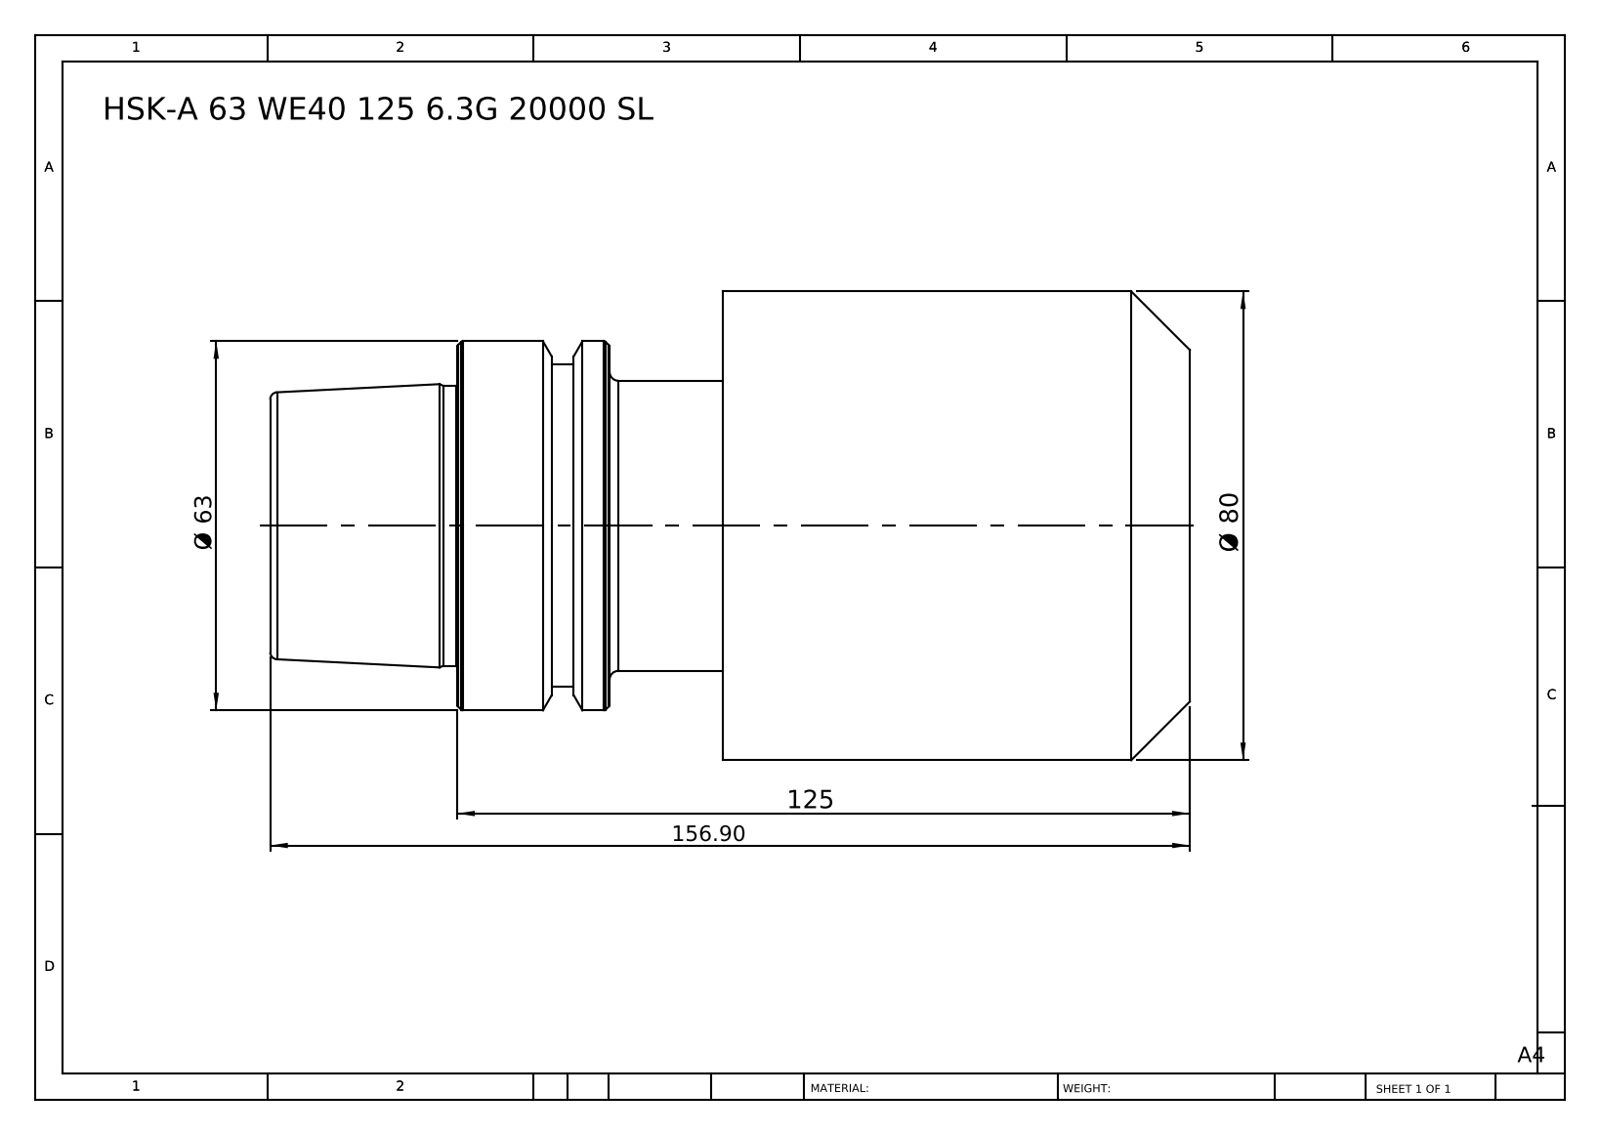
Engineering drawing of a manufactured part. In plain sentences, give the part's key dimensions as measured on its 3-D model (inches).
The part is named "HSK-A 63 WE40 125 6.3G 20000 SL". Its 3-D file was written by "SolidWorks 2014 (CONFIG_CONTROL_DESIGN)". It is 1 solid with 49 faces: 7 planar, 12 cylindrical and 30 other. Overall it measures 6.177 by 3.15 by 3.15 inches. Its volume is 34.09 cubic inches and its surface area 68.47 square inches. Round bosses or shafts: 1 of diameter 3.15, 1 of diameter 2.48, 1 of diameter 2.165, 1 of diameter 1.949, 1 of diameter 1.881. The main face-to-face distances are 3.135, 6.177, 3.043, 3.898, 0.763, 2.28, 4.921, 1.787, 1.024, 1.256.
